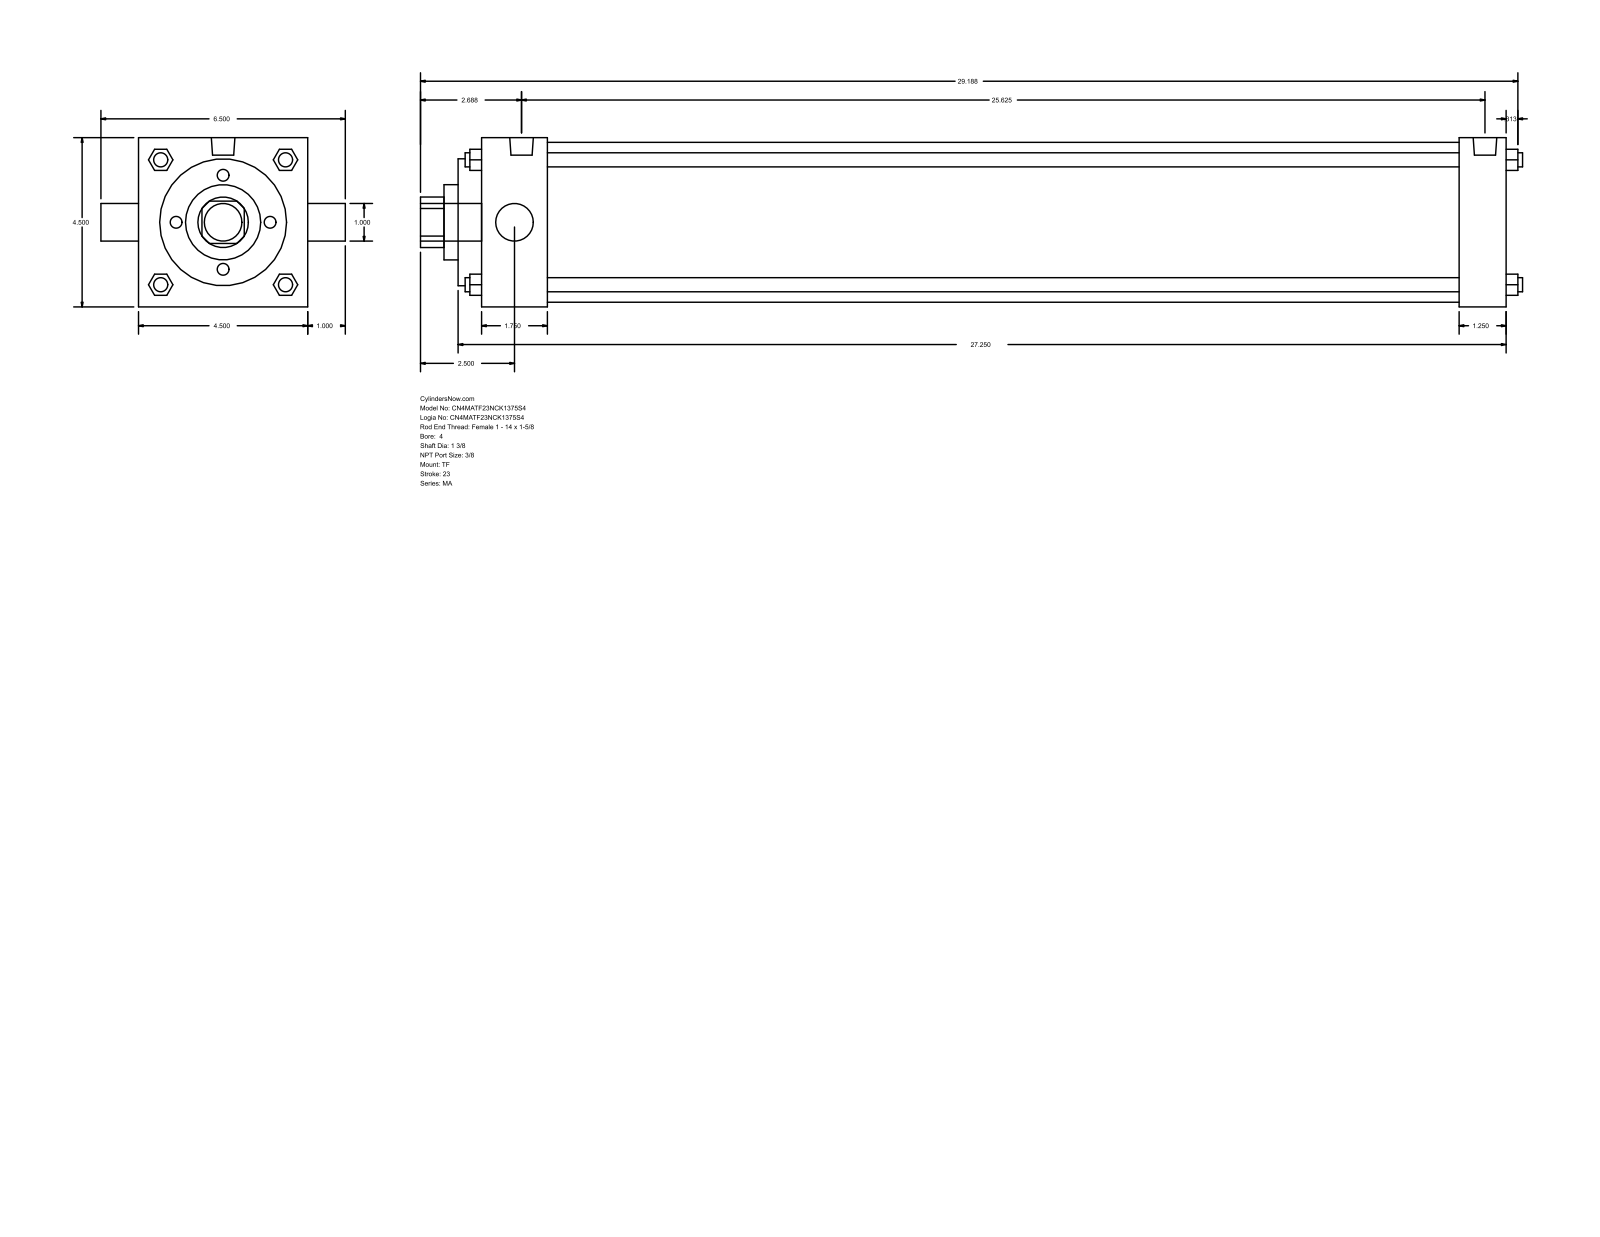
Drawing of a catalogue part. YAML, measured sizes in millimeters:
part_name: "MA_TF__0400_1.375"
step_written_by: "GSSL Pune (CONFIG_CONTROL_DESIGN)"
units: millimeters
bodies: {solids: 0, faces: 122, planar: 93, cylindrical: 29, other: 0}
overall_size: [744.54, 165.1, 114.3]
round_holes:
  - {diameter: 25.4, count: 1}
  - {diameter: 34.92, count: 1}
  - {diameter: 50.8, count: 1}
  - {diameter: 85.72, count: 1}
  - {diameter: 107.95, count: 1}
round_bosses_or_shafts:
  - {diameter: 9.53, count: 4}
  - {diameter: 11.11, count: 3}
  - {diameter: 15.93, count: 2}
  - {diameter: 25.4, count: 1}
partial_cylinders:
  - {radius: 17.06, count: 1}
face_to_face_distances: [114.3, 692.15, 708.02, 15.87, 676.27, 660.4, 31.75, 60.32, 44.45, 615.95]
